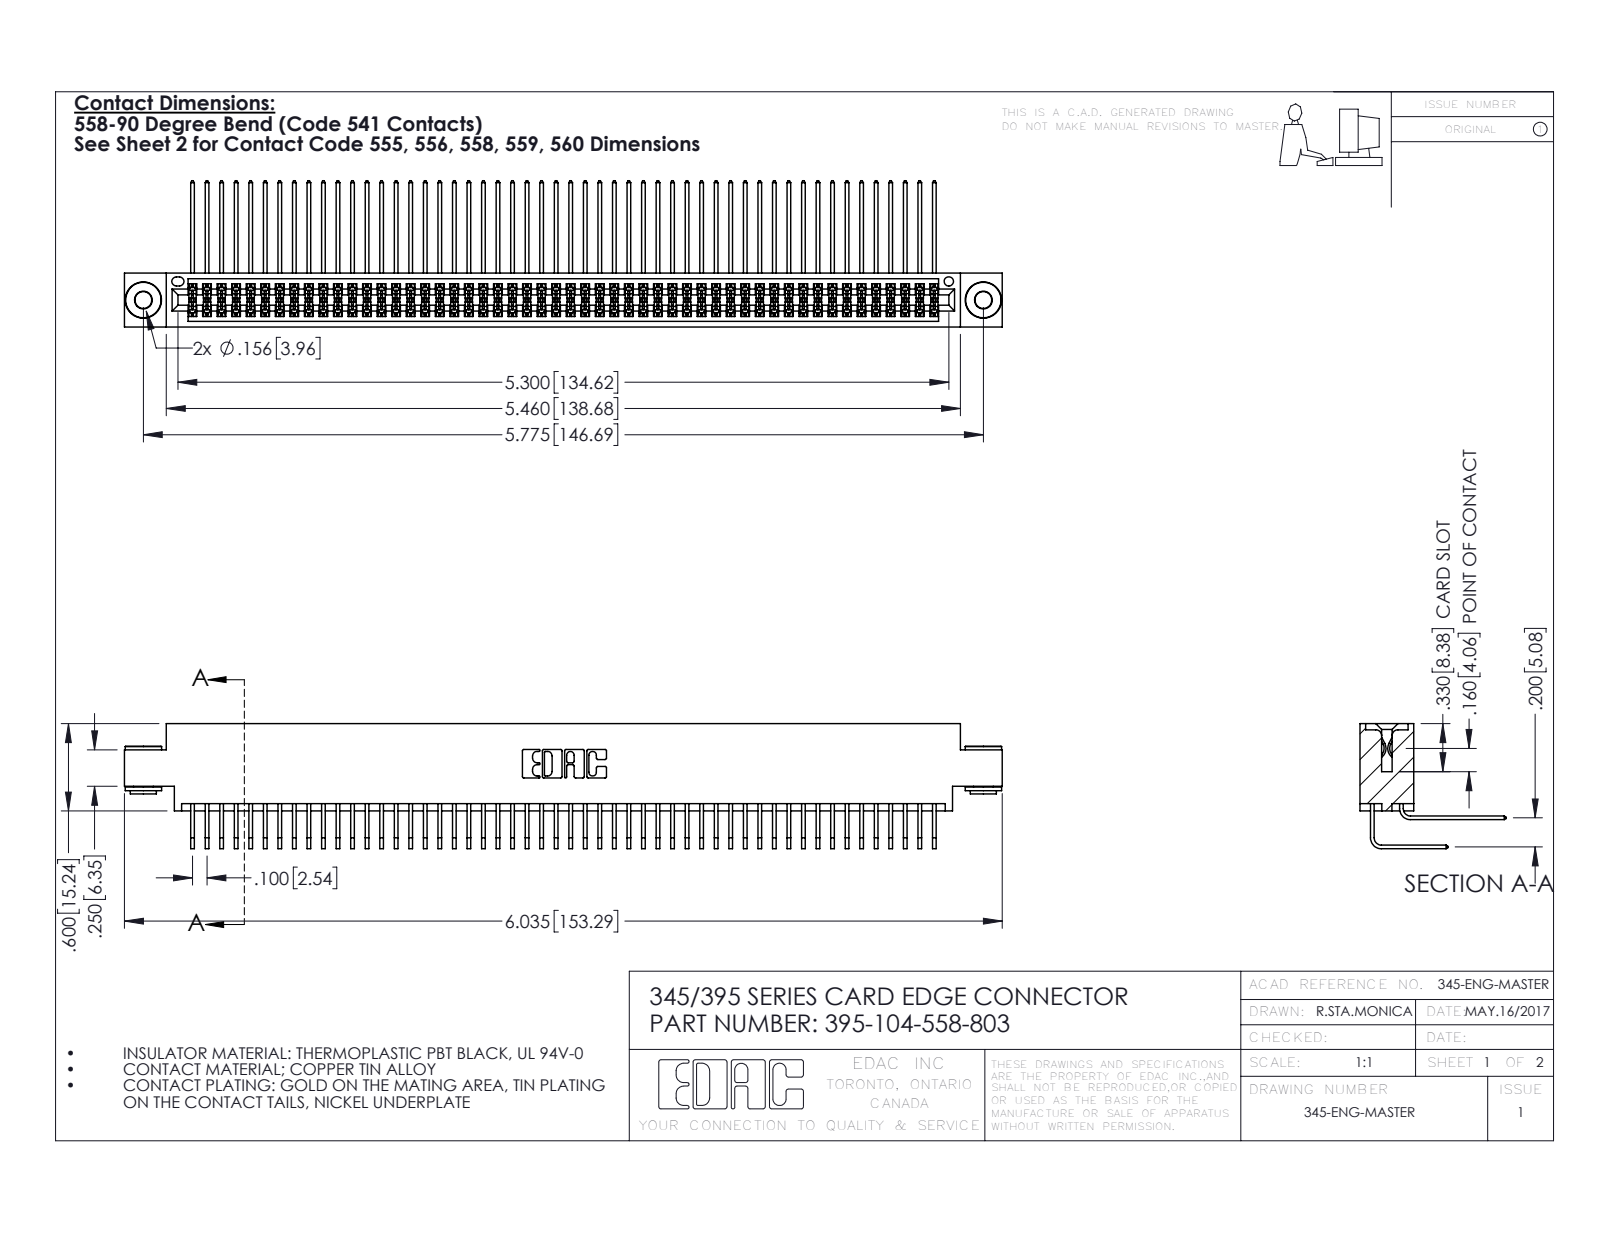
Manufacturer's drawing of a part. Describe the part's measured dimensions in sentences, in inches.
The part is named "345 Part_0.170 Offset - 0.156 Dia-TH; 345-292-001_558 559 Tail - 1; 395-104-558-803; 345-292-001_558 Tail - 2 (+1 more)". Its 3-D file was written by "SolidWorks 2016 (CONFIG_CONTROL_DESIGN)". It is 107 solids with 5576 faces: 3734 planar, 1834 cylindrical and 8 other. Overall it measures 6.035 by 1.005 by 0.859 inches. Its volume is 0.945 cubic inches and its surface area 40.7 square inches. Round holes: 2 of diameter 0.116, 2 of diameter 0.156, 1 of diameter 0.064. Round bosses or shafts: 2 of diameter 0.25, 2 of diameter 0.18, 2 of diameter 0.136. Partial cylindrical surfaces (rounded edges, fillets, slot ends): 157 of radius 0.006, 22 of radius 0.01, 6 of radius 0.007, 6 of radius 0.031, 3 of radius 0.026, 2 of radius 0.014, 2 of radius 0.019, 2 of radius 0.022. The main face-to-face distances are 0.072, 0.298, 0.2, 0.37, 0.098, 0.272, 0.025, 0.225, 0.175, 0.025. The hole center spacings are 0.27, 5.539, 5.775.
